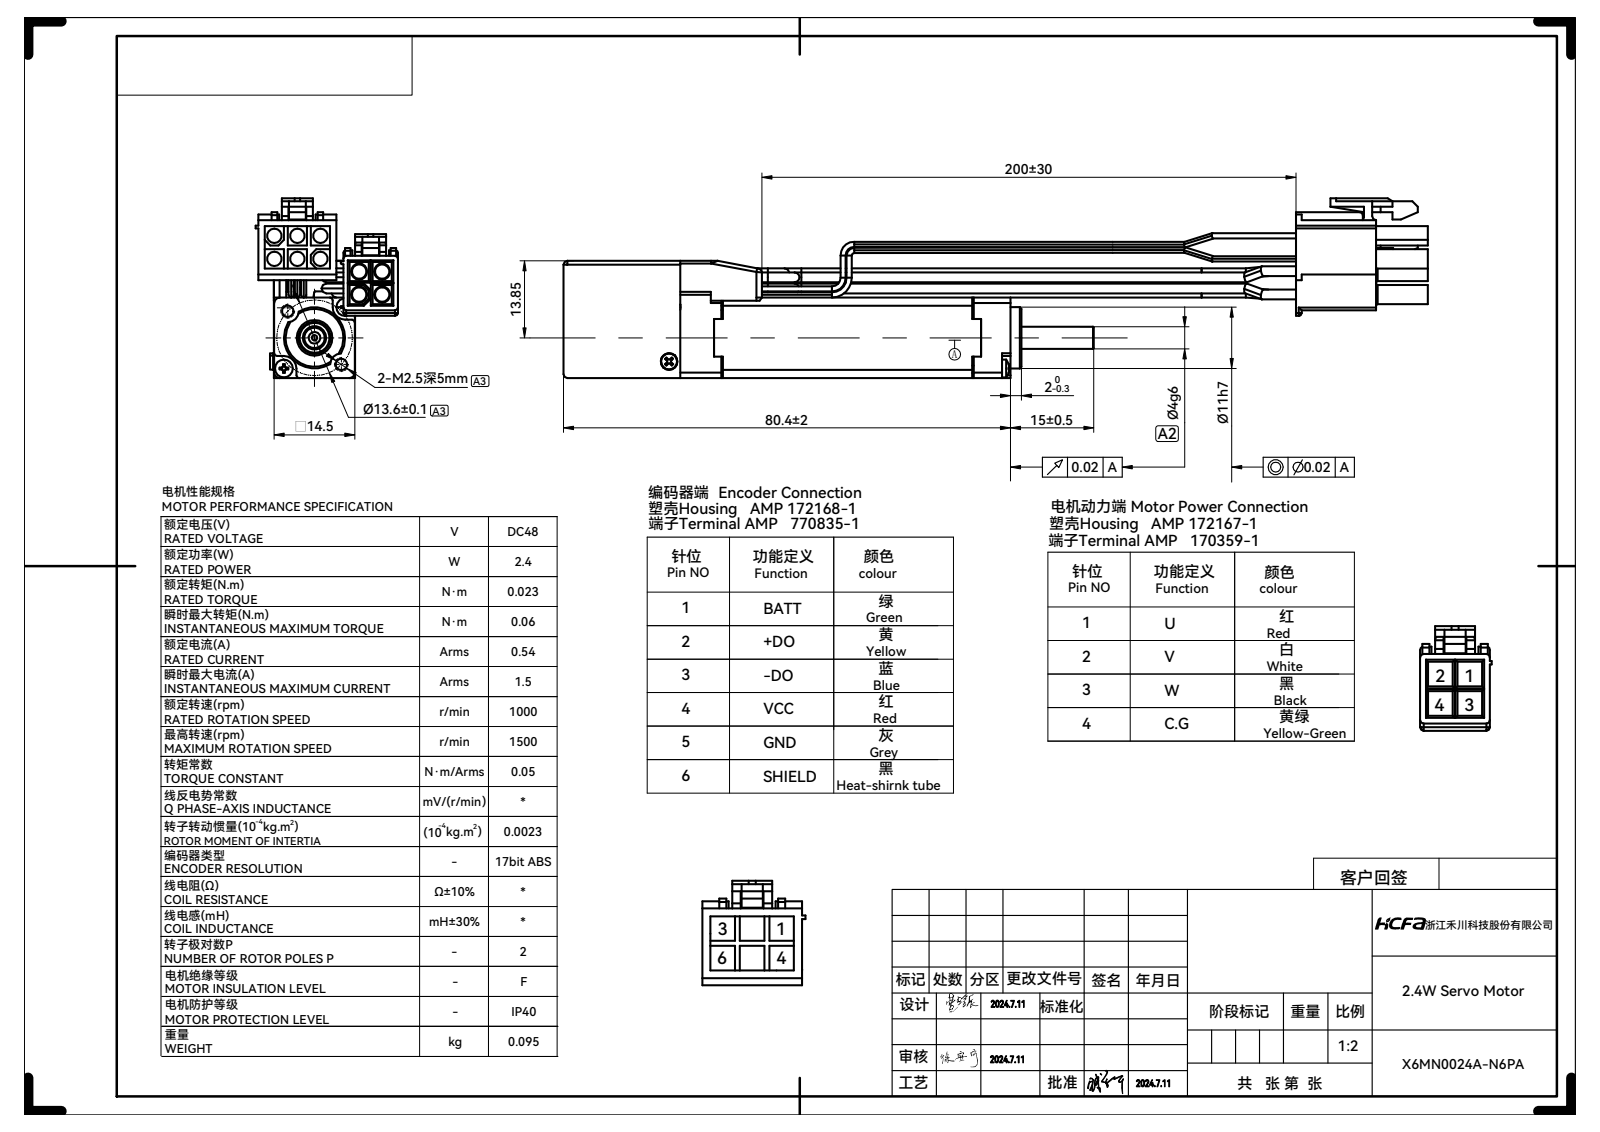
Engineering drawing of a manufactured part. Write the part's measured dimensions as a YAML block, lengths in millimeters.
part_name: "SV-X6MN0024A-N6PA001"
step_written_by: "ZW3D to STEP translator (AUTOMOTIVE_DESIGN)"
units: millimeters
bodies: {solids: 1, faces: 1036, planar: 679, cylindrical: 286, other: 71}
overall_size: [154.68, 31.79, 25.58]
volume: 20451
surface_area: 18137
round_holes:
  - {diameter: 1.8, count: 2}
  - {diameter: 2.5, count: 2}
  - {diameter: 13.2, count: 1}
round_bosses_or_shafts:
  - {diameter: 0.98, count: 27}
  - {diameter: 1.76, count: 20}
  - {diameter: 3.2, count: 2}
  - {diameter: 1.6, count: 2}
  - {diameter: 11, count: 1}
  - {diameter: 5, count: 1}
  - {diameter: 4, count: 1}
partial_cylinders:
  - {radius: 0.3, count: 32}
  - {radius: 0.5, count: 30}
  - {radius: 0.2, count: 10}
  - {radius: 0.7, count: 9}
  - {radius: 1, count: 6}
  - {radius: 1.5, count: 5}
  - {radius: 0.1, count: 4}
  - {radius: 0.9, count: 4}
face_to_face_distances: [0.6, 14.5, 14.56, 0.54, 13.96, 14.02, 20.5, 4.14, 3.45, 13.42]
hole_center_spacings: [6.8, 7.81, 10.28, 10.43, 13.61, 15.61]
